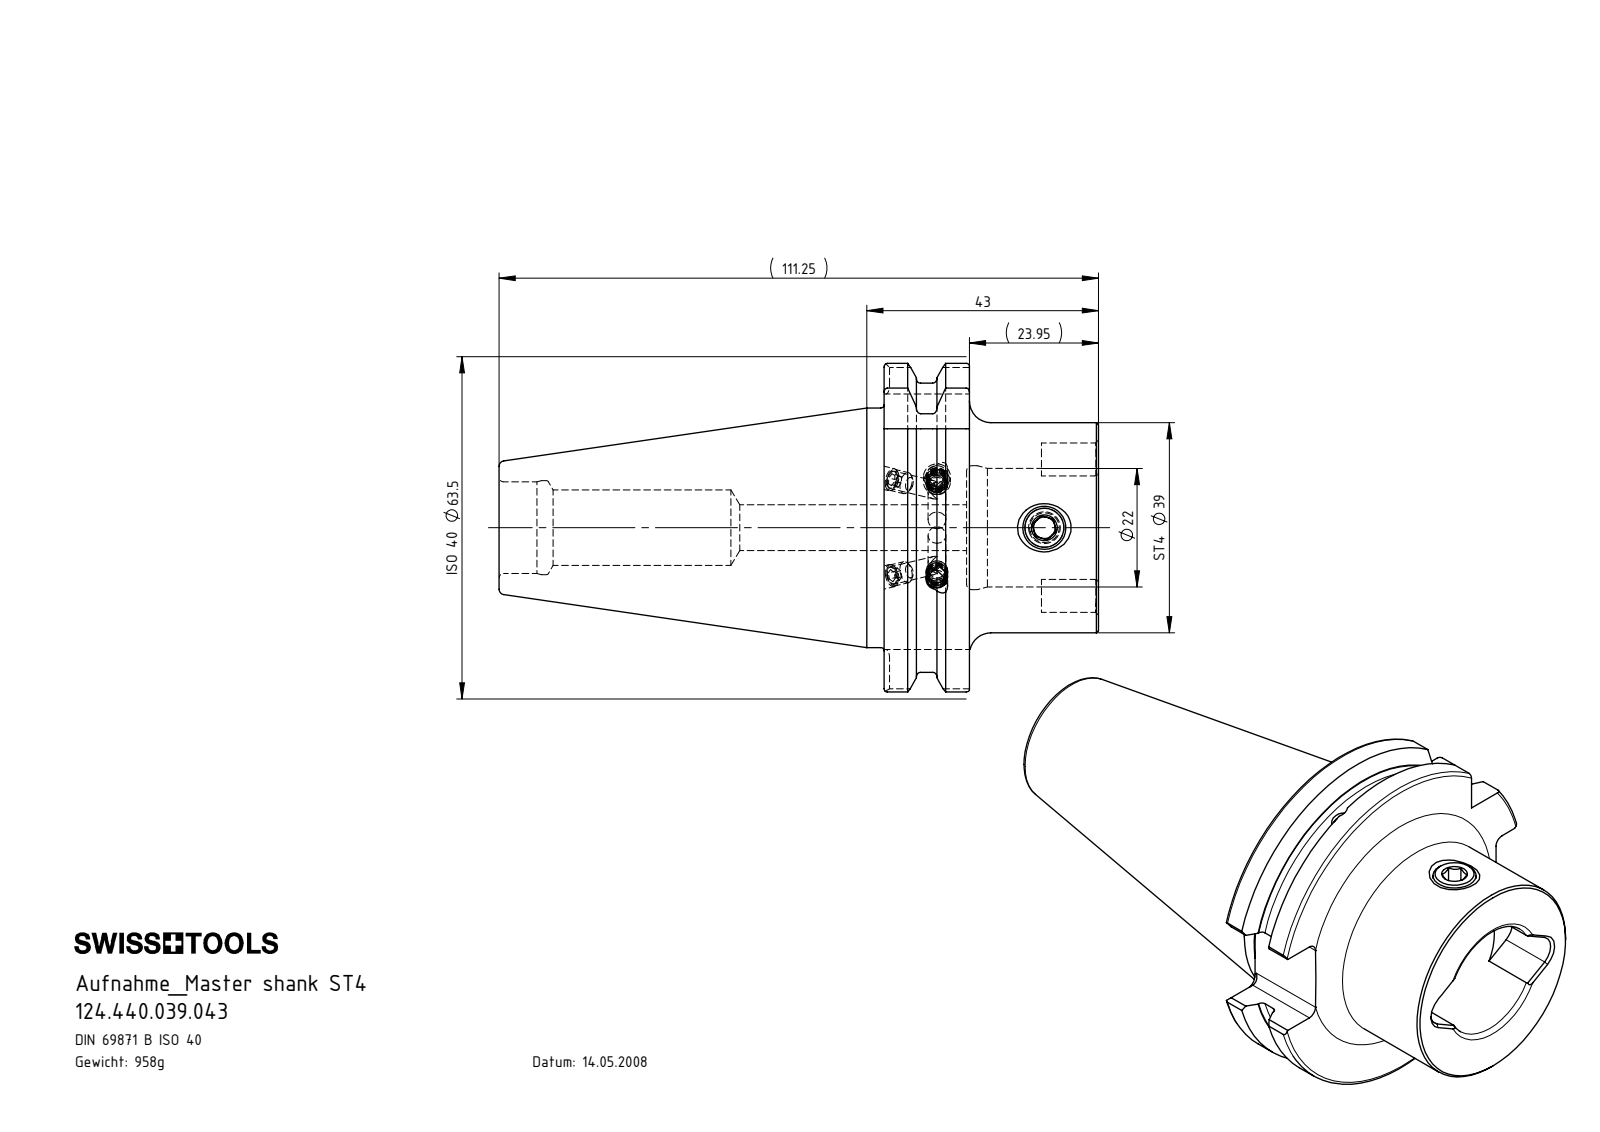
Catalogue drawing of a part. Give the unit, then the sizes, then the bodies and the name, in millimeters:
Units: millimetres
Overall size (bounding box): 111.25 × 63.5 × 60.94
Round holes (diameter × count): ⌀3.3 ×3, ⌀3 ×2, ⌀4 ×2, ⌀4.2 ×2, ⌀7.25 ×1, ⌀8.5 ×1, ⌀14 ×1, ⌀17 ×1, ⌀17.45 ×1, ⌀22 ×1, ⌀23 ×1
Round bosses / shafts (diameter × count): ⌀4 ×4, ⌀44.45 ×1, ⌀39 ×1, ⌀8 ×1, ⌀5 ×1
Partial cylindrical surfaces — rounded edges, fillets, slot ends (radius × count): R1.6 ×8, R3.2 ×2, R28 ×1, R31.75 ×1
Main face-to-face distances: 15.85, 39.8, 23.95, 15.3, 0.55, 24.5, 47.4, 71.45, 86.75, 87.3
Volume: 122 135 mm³ · Surface area: 25 716 mm²
Bodies: 9 solids, 218 faces (87 planar, 51 cylindrical, 80 other)
Part name (STEP PRODUCT): ISO 4026 - M5 x 4; ISO 4026 - M4 x 4_PreviewCfg; ST4-ER1.001.011_A; KVT_MB_600_040 (+2 more)
STEP written by: SolidWorks 2017 (AUTOMOTIVE_DESIGN)
